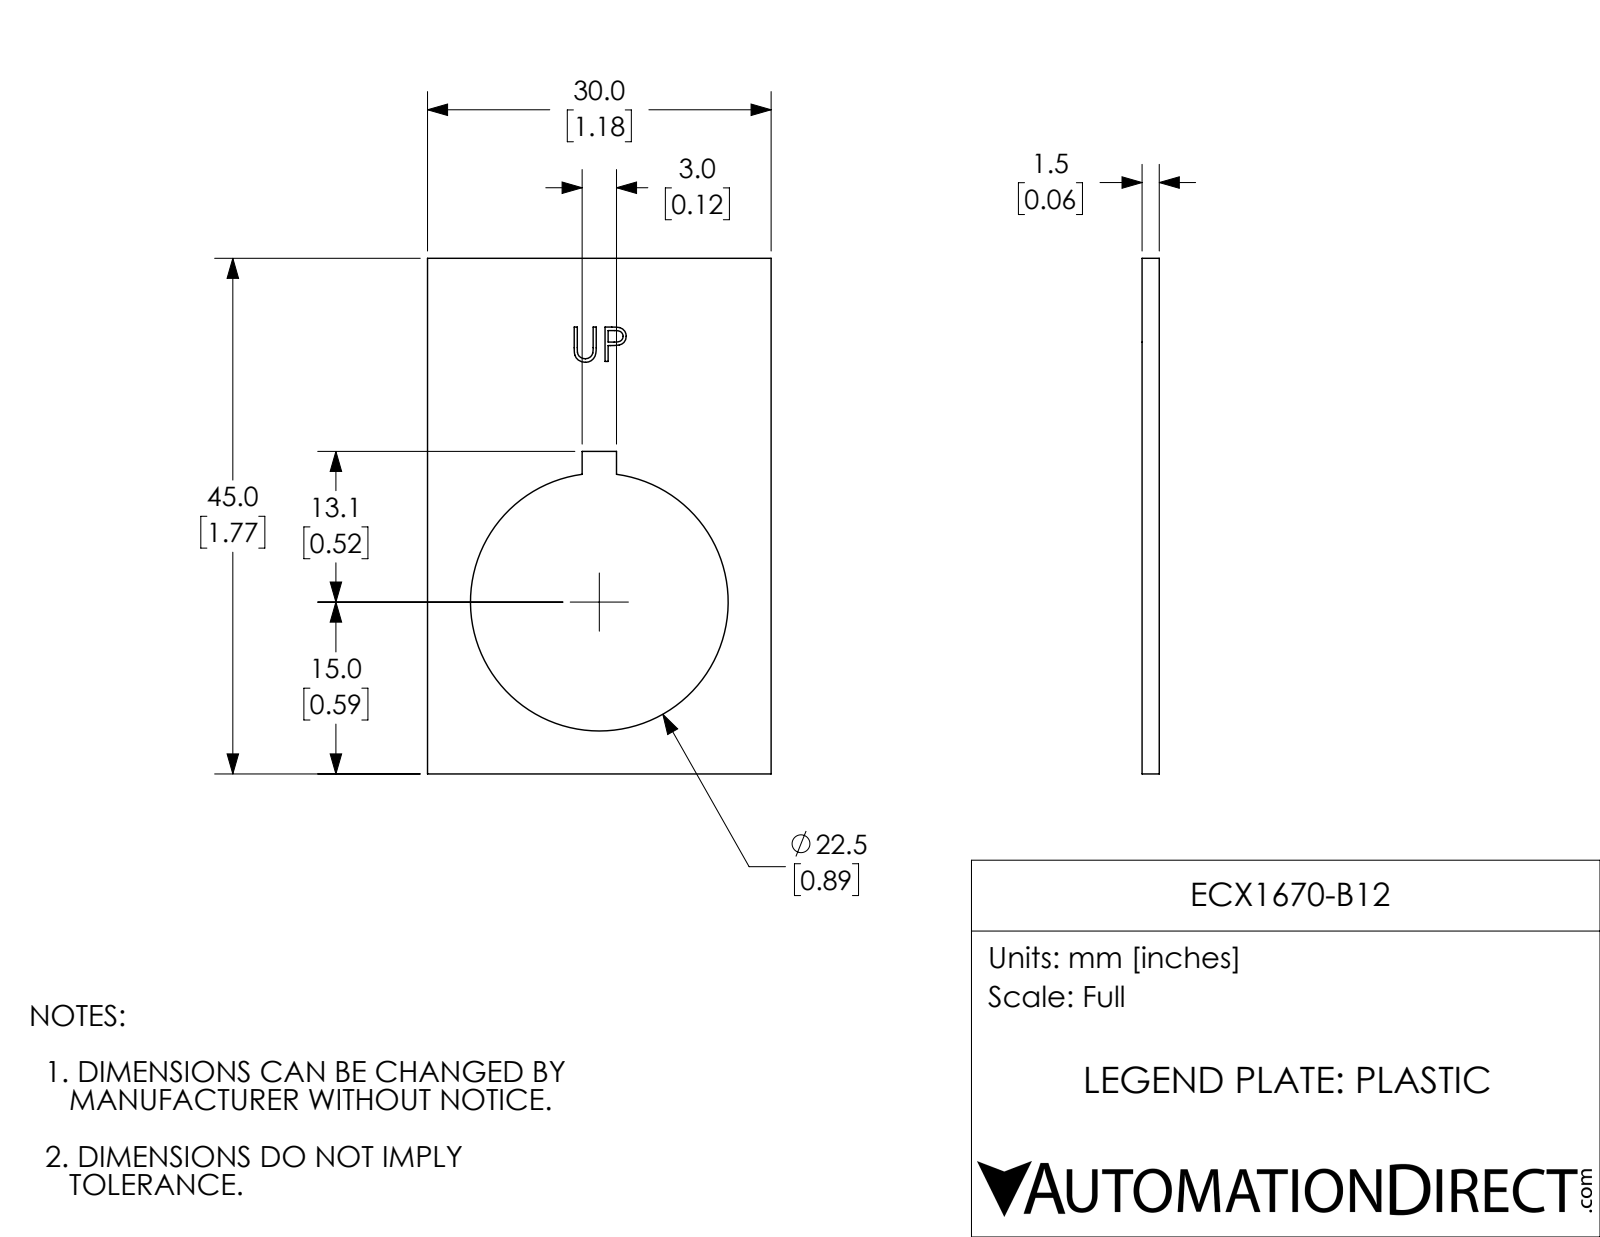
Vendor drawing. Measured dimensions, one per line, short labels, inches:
name: ECX1670-B12
written by: SolidWorks 2017 (AUTOMOTIVE_DESIGN)
unit: in
bodies: 1 solid, 42 faces (26 planar, 3 cylindrical, 13 other)
size: 1.772 × 1.181 × 0.059
volume: 0.087 in³; area: 3.458 in²
holes: 1× ⌀0.886
face distances: 0.059, 1.181, 1.772, 0.531, 0.65, 1.108, 0.663, 0.058, 0.118, 0.106
